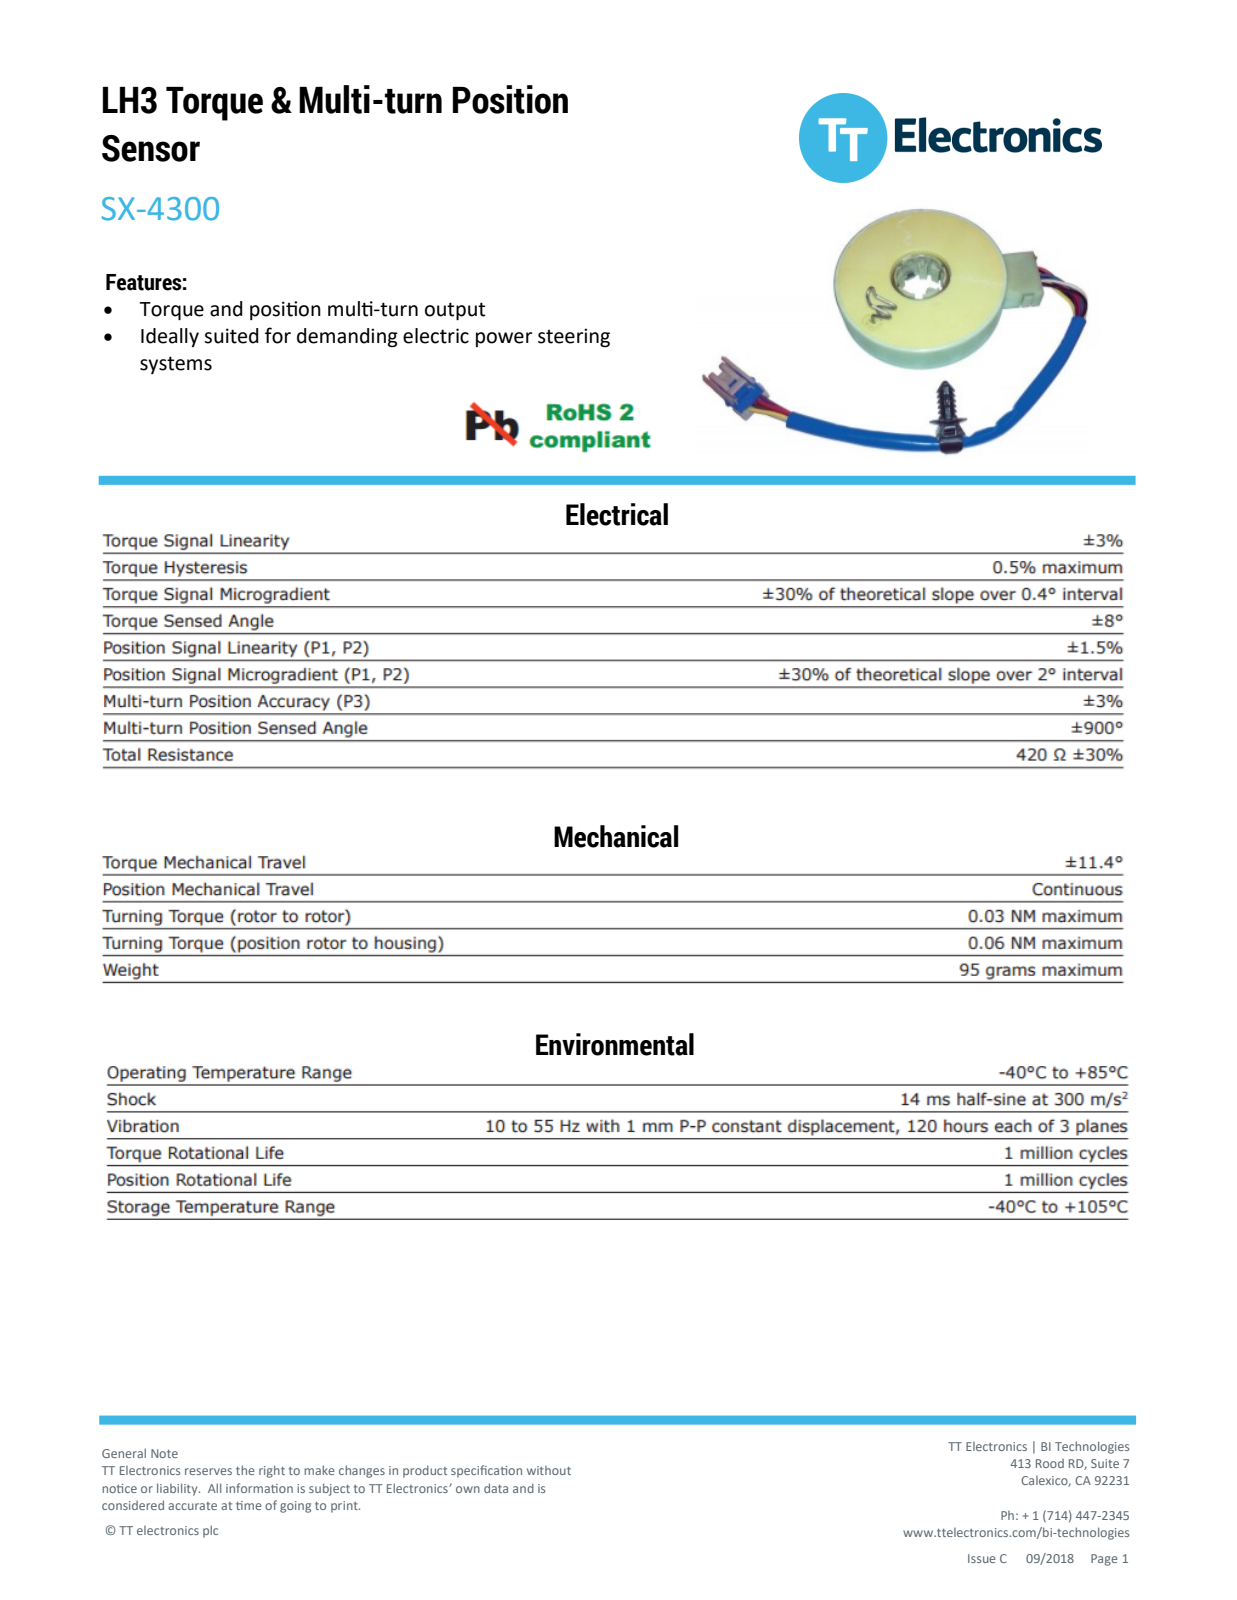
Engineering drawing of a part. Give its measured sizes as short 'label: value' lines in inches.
name: SX-4286B_SW0001
written by: PRO/ENGINEER BY PARAMETRIC TECHNOLOGY CORPORATION, 2012230 (CONFIG_CONTROL_DESIGN)
unit: in
bodies: 3 solids, 1492 faces (681 planar, 519 cylindrical, 292 other)
size: 14.169 × 5.134 × 1.839
volume: 6.575 in³; area: 52.9 in²
holes: 1× ⌀1.046, 1× ⌀1.126, 1× ⌀1.146, 1× ⌀1.2, 1× ⌀1.255, 1× ⌀3.15
bosses: 6× ⌀0.047, 2× ⌀0.35, 1× ⌀3.2, 1× ⌀3.142, 1× ⌀3.056, 1× ⌀1.345, 1× ⌀1.234, 1× ⌀0.53
rounds: 72× R0.007, 72× R0.012, 38× R0.005, 32× R0.01, 22× R0.02, 19× R0.016, 18× R0.006, 18× R0.028
face distances: 0.719, 0.065, 0.047, 0.012, 0.114, 0.729, 0.077, 0.796, 0.806, 0.055
